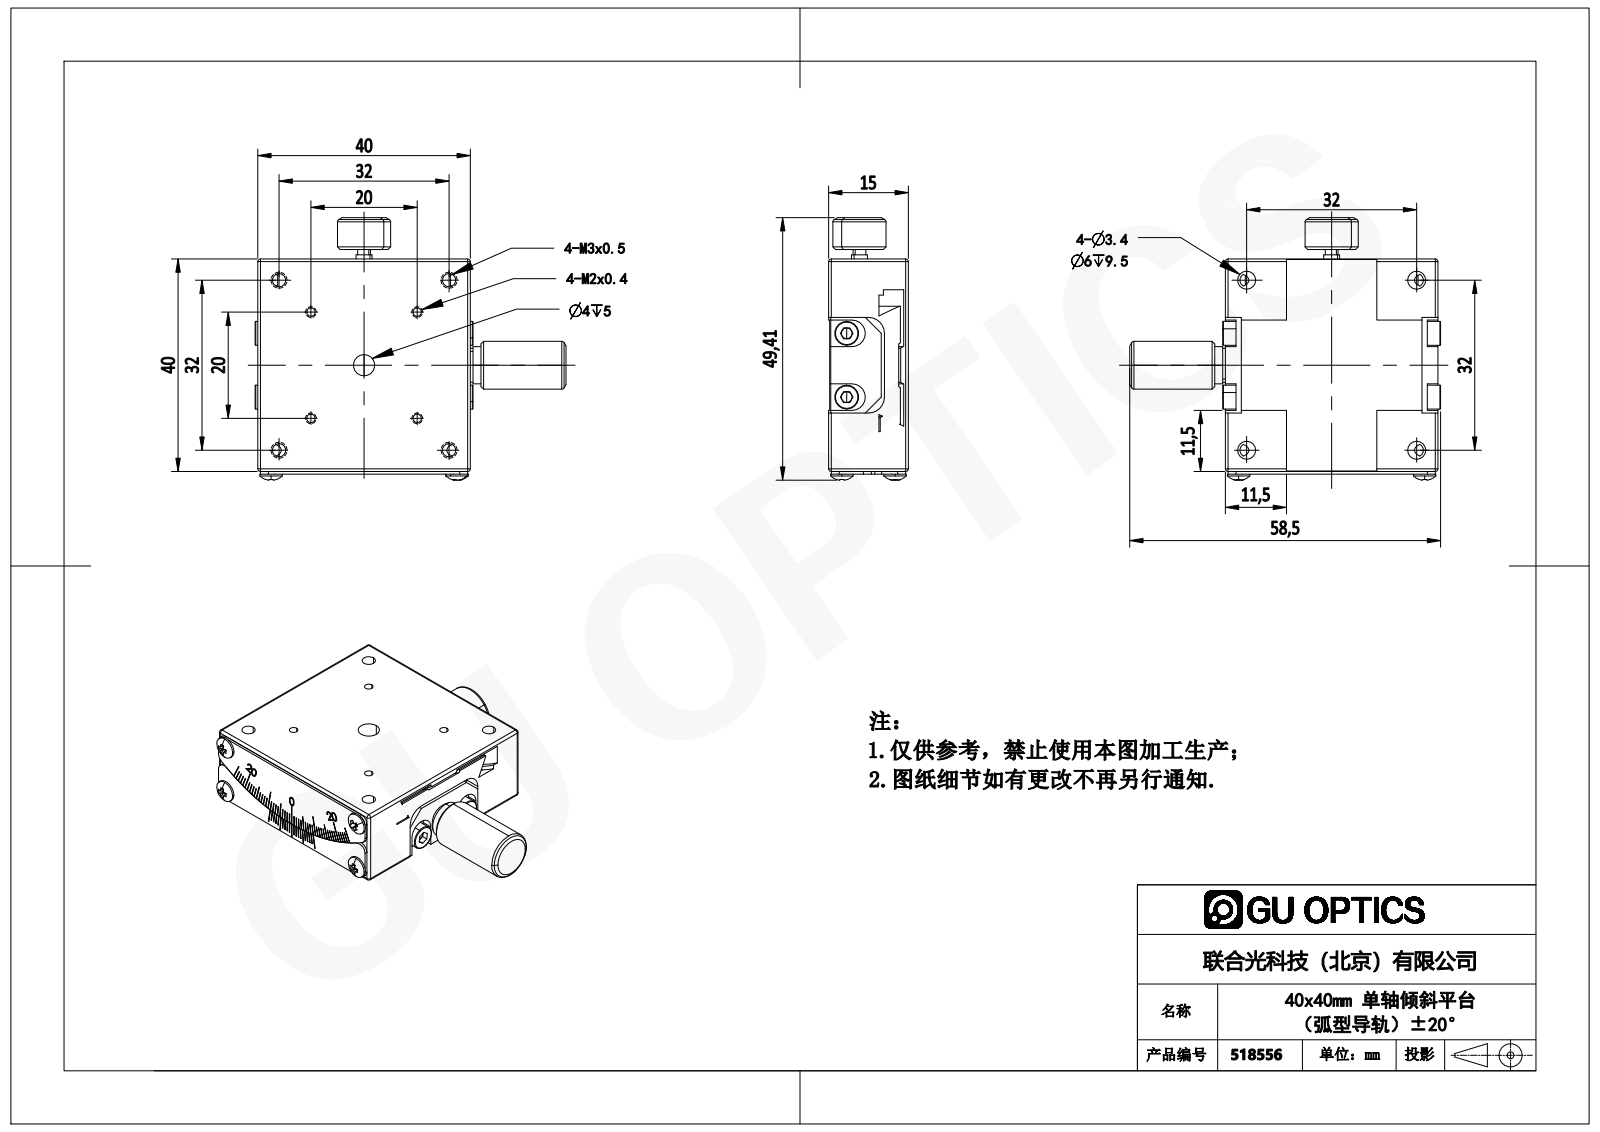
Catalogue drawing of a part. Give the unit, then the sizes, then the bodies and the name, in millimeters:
Units: millimetres
Overall size (bounding box): 58.5 × 49.41 × 15
Round holes (diameter × count): ⌀2.5 ×6, ⌀1.6 ×4, ⌀3.4 ×4, ⌀6 ×4, ⌀4 ×2
Round bosses / shafts (diameter × count): ⌀4.2 ×4, ⌀4.5 ×2, ⌀2 ×2, ⌀10 ×1, ⌀9 ×1, ⌀7 ×1, ⌀6.4 ×1, ⌀3 ×1
Partial cylindrical surfaces — rounded edges, fillets, slot ends (radius × count): R0.5 ×12, R1.5 ×8, R1.25 ×2, R2.5 ×2, R3 ×2, R2.9 ×1, R32.7 ×1, R33 ×1
Main face-to-face distances: 40, 14.8, 0.5, 40.5, 15, 5.8, 34.2, 34.7, 4, 14.6
Hole centre spacings: 26.68, 8.49, 14.14, 20, 22.63, 32, 36.77, 28.28
Volume: 23 730 mm³ · Surface area: 11 812 mm²
Bodies: 5 solids, 866 faces (604 planar, 125 cylindrical, 137 other)
Part name (STEP PRODUCT): MXG4-25CS
STEP written by: SolidWorks 2020 (CONFIG_CONTROL_DESIGN)
